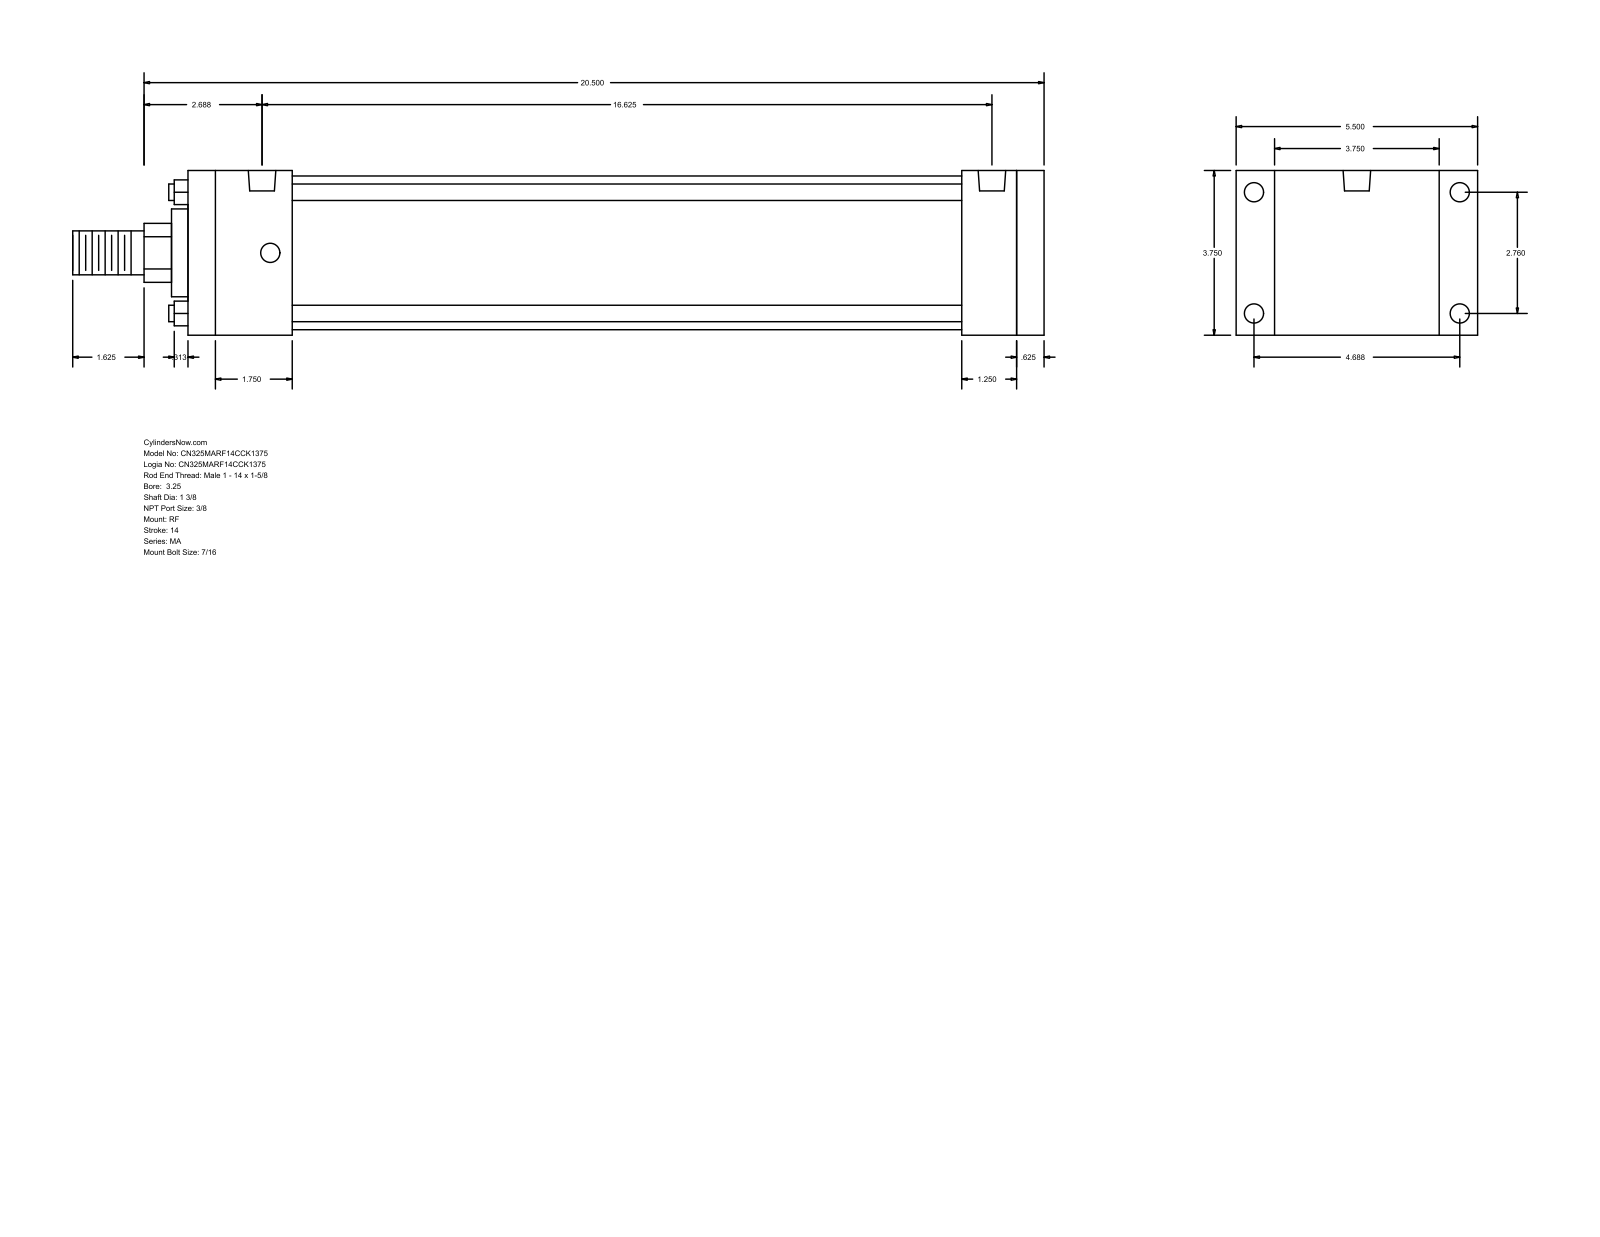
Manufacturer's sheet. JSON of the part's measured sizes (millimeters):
{"part_name": "MA_RF__0325_1.375", "step_written_by": "GSSL Pune (CONFIG_CONTROL_DESIGN)", "units": "millimeters", "bodies": {"solids": 0, "faces": 92, "planar": 64, "cylindrical": 28, "other": 0}, "overall_size": [561.98, 139.7, 95.25], "round_holes": [[11.11, 8], [15.93, 2]], "round_bosses_or_shafts": [[9.53, 4], [88.9, 1], [50.8, 1], [34.92, 1], [25.4, 1]], "partial_cylinders_radius": [[17.06, 1]], "face_to_face_distances": [95.24, 495.3, 15.88, 479.42, 22.23, 117.47, 447.67, 31.75, 47.63, 60.32], "hole_center_spacings": [4.77, 70.1, 119.06, 138.16, 412.74, 417.51, 422.28]}
